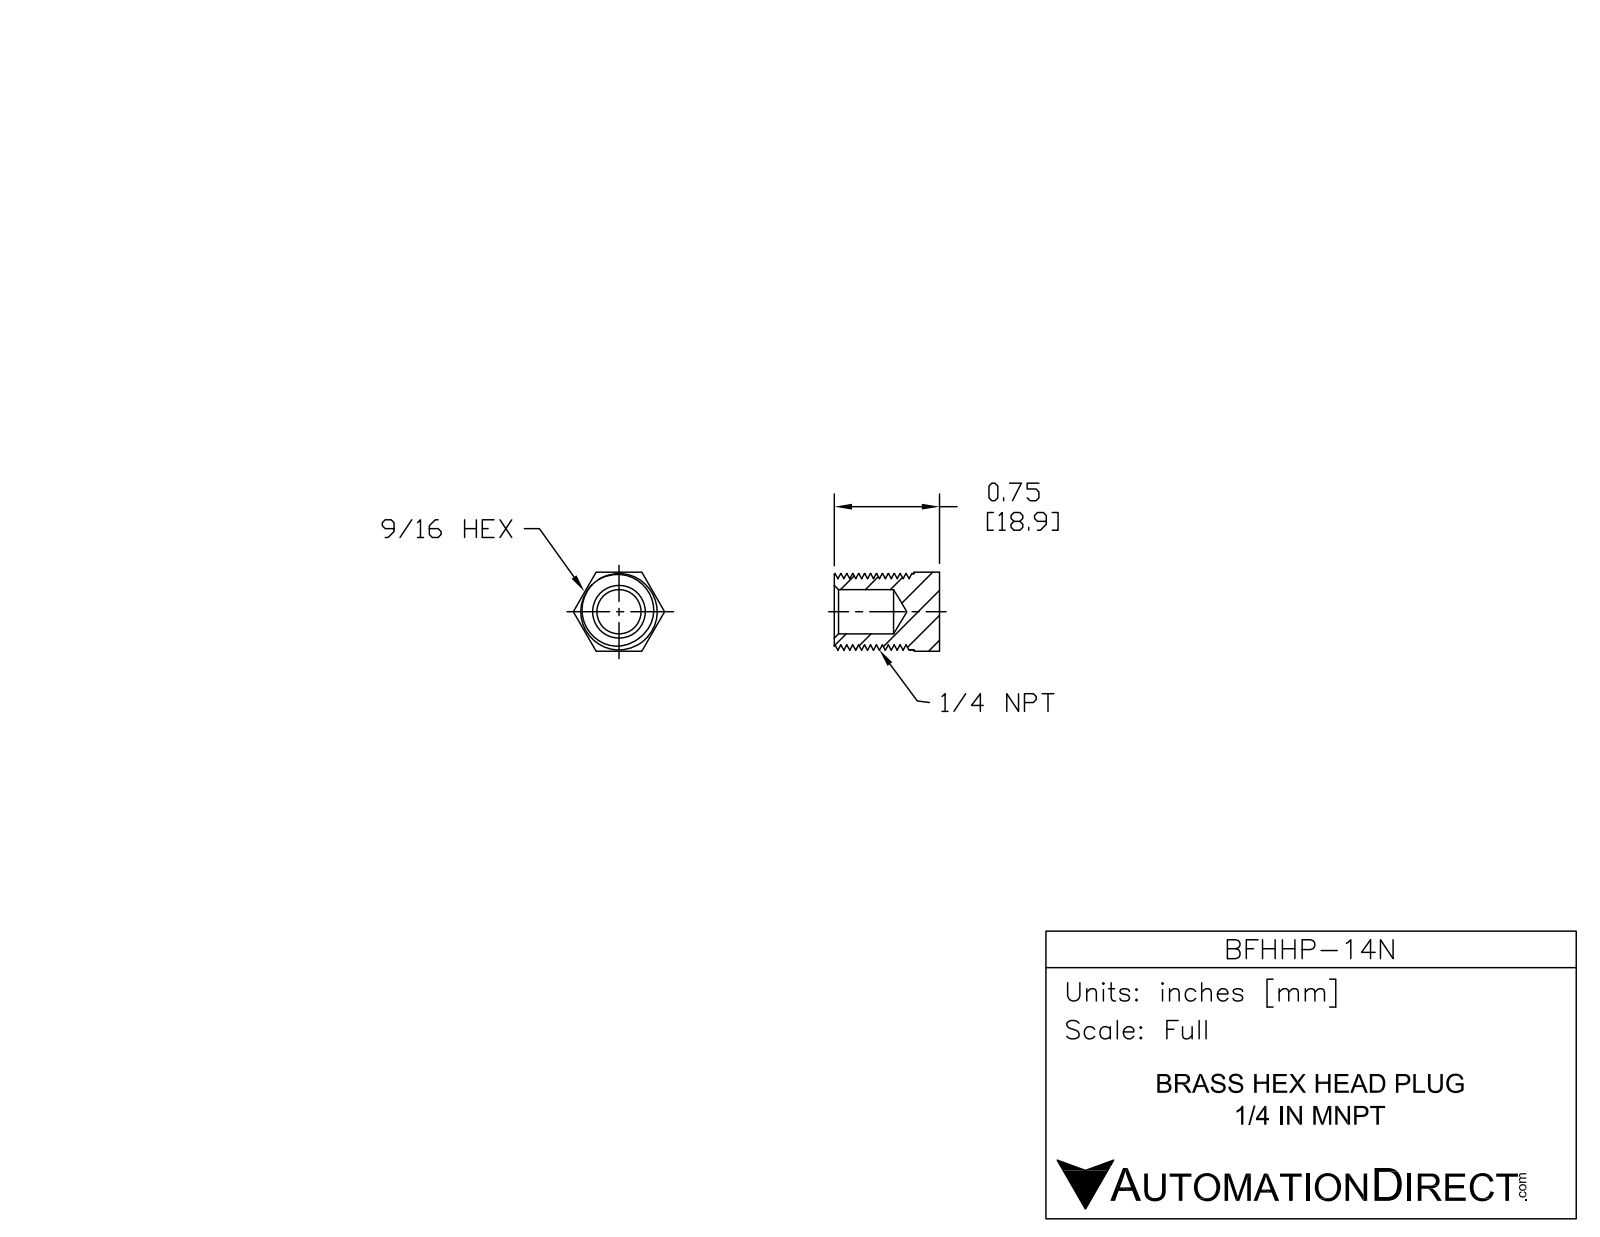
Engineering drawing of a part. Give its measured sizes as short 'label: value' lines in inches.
name: BFHHP-14N
written by: SolidWorks 2015 (CONFIG_CONTROL_DESIGN)
unit: in
bodies: 1 solid, 47 faces (10 planar, 30 cylindrical, 7 other)
size: 0.745 × 0.647 × 0.56
volume: 0.128 in³; area: 3.007 in²
holes: 1× ⌀0.313
bosses: 1× ⌀0.54
face distances: 0.56, 0.745, 0.18, 0.565
